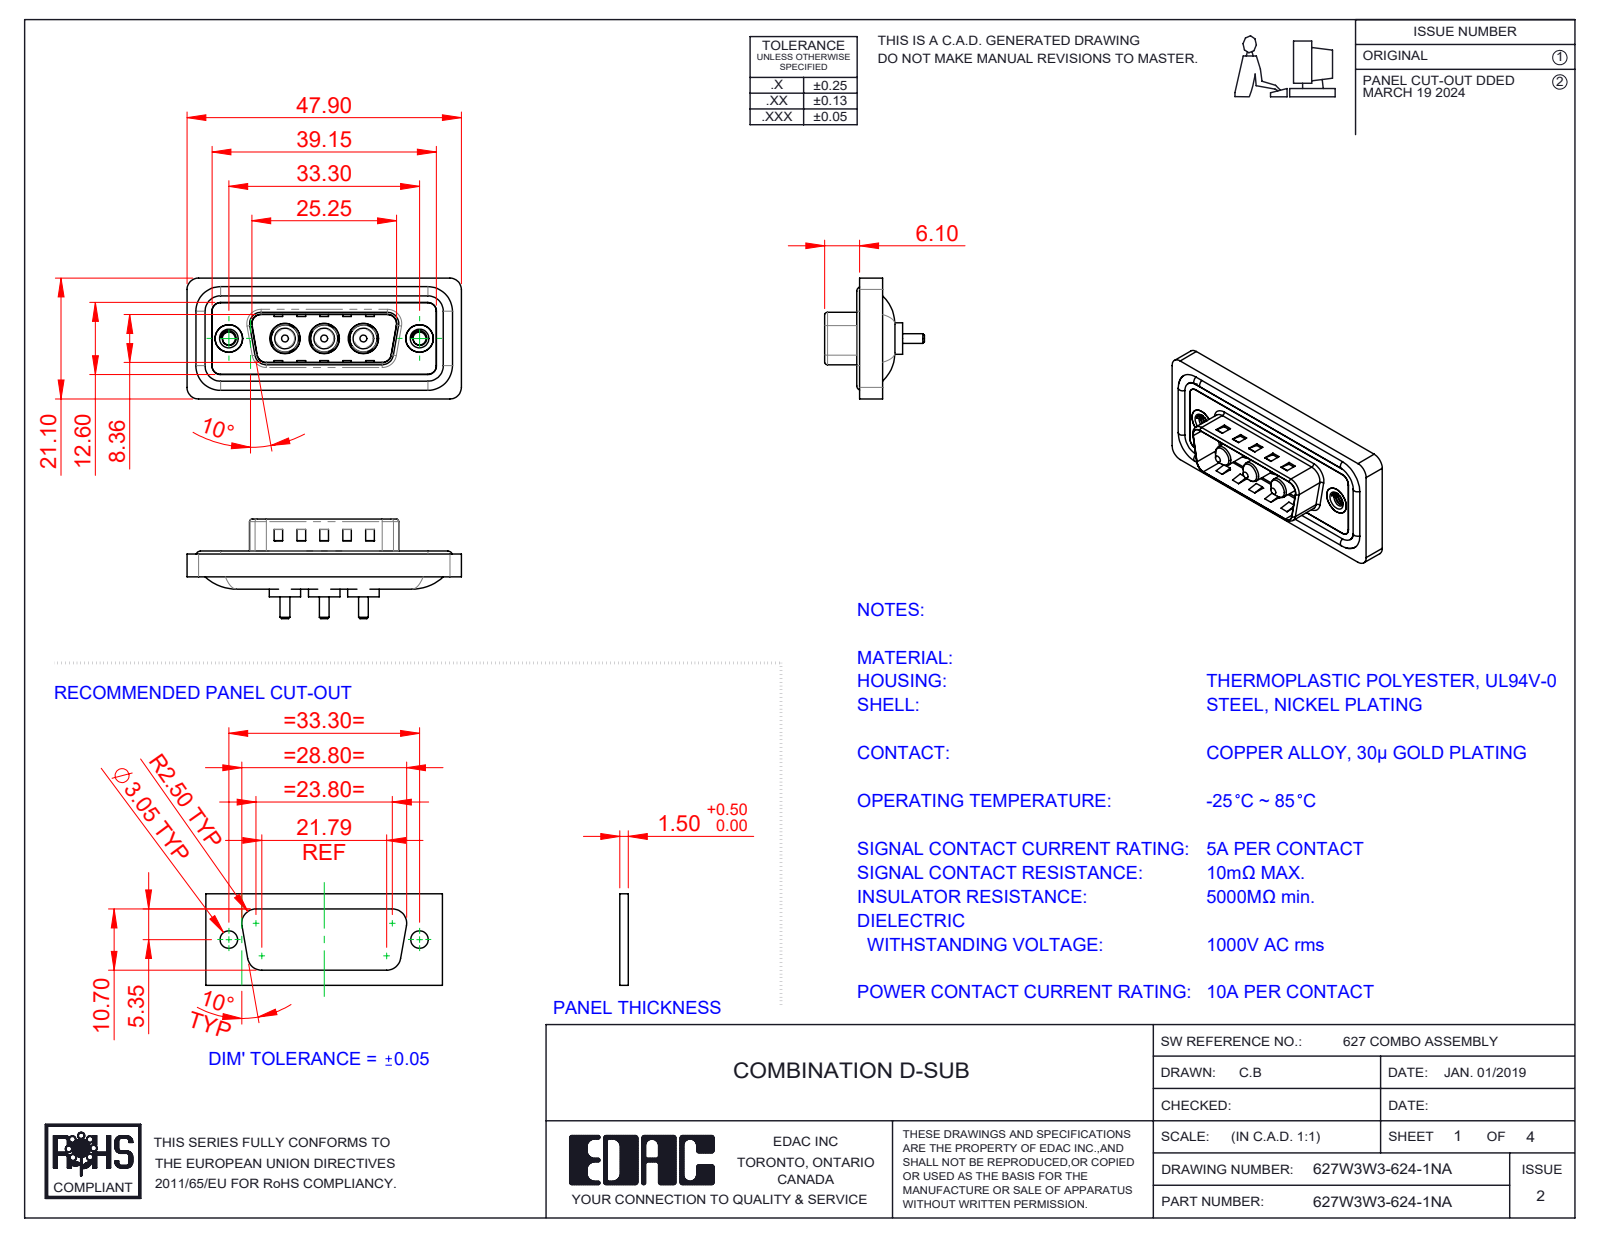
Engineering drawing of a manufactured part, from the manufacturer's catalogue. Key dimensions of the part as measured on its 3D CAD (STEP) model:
Part name (STEP PRODUCT): 627Combo Waterproof Housing_15 Contacts; 627Combo Housing_3W3; 627Combo Threaded Rivet_A; 627W3W3-624-1NA (+3 more)
STEP written by: SolidWorks 2023 (CONFIG_CONTROL_DESIGN)
Units: millimetres
Bodies: 13 solids, 562 faces (207 planar, 243 cylindrical, 112 other)
Overall size (bounding box): 47.9 × 21.1 × 17.4
Volume: 5 543 mm³ · Surface area: 8 713 mm²
Round holes (diameter × count): ⌀4.85 ×3, ⌀5.3 ×3, ⌀2.26 ×2, ⌀4 ×2, ⌀4.8 ×2, ⌀5 ×2
Round bosses / shafts (diameter × count): ⌀1.6 ×4, ⌀5.5 ×3, ⌀5.2 ×3, ⌀4.75 ×3, ⌀3.75 ×3, ⌀3.6 ×3, ⌀1.7 ×3, ⌀4.9 ×2
Partial cylindrical surfaces — rounded edges, fillets, slot ends (radius × count): R1.5 ×26, R2 ×20, R0.5 ×8, R1.6 ×8, R0.25 ×4, R0.6 ×4, R0.65 ×4, R0.9 ×4
Main face-to-face distances: 0.4, 1.5, 1.1, 0.5, 1.6, 3.1, 2.9, 4, 0.82, 9.58
Hole centre spacings: 6.85, 9.8, 16.65, 23.5, 13.7, 33.3
